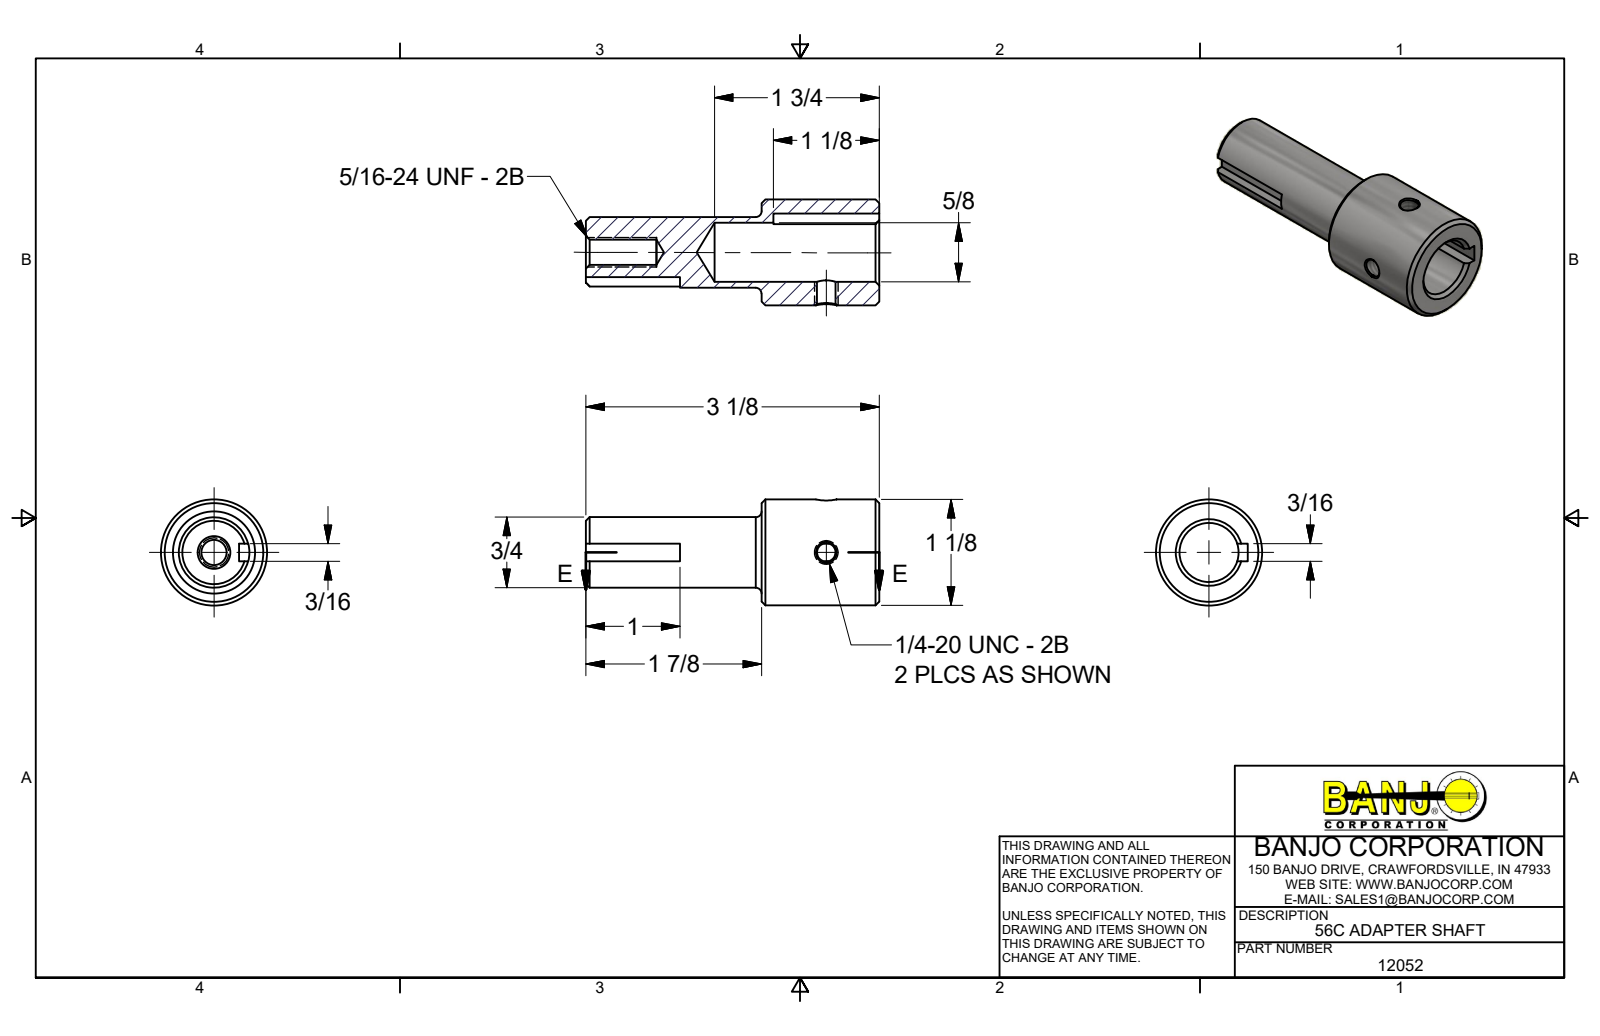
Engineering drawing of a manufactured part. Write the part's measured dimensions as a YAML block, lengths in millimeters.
part_name: "12052"
step_written_by: "Autodesk Inventor 2017 (AUTOMOTIVE_DESIGN)"
units: millimeters
bodies: {solids: 1, faces: 27, planar: 11, cylindrical: 6, other: 10}
overall_size: [79.15, 28.58, 28.57]
volume: 22927
surface_area: 9820
round_holes:
  - {diameter: 4.98, count: 2}
  - {diameter: 6.78, count: 1}
  - {diameter: 15.93, count: 1}
round_bosses_or_shafts:
  - {diameter: 28.57, count: 1}
  - {diameter: 19.05, count: 1}
face_to_face_distances: [31.75, 47.4, 79.15, 4.78, 17.17, 25.4, 22, 53.75, 50.57, 25.17]
